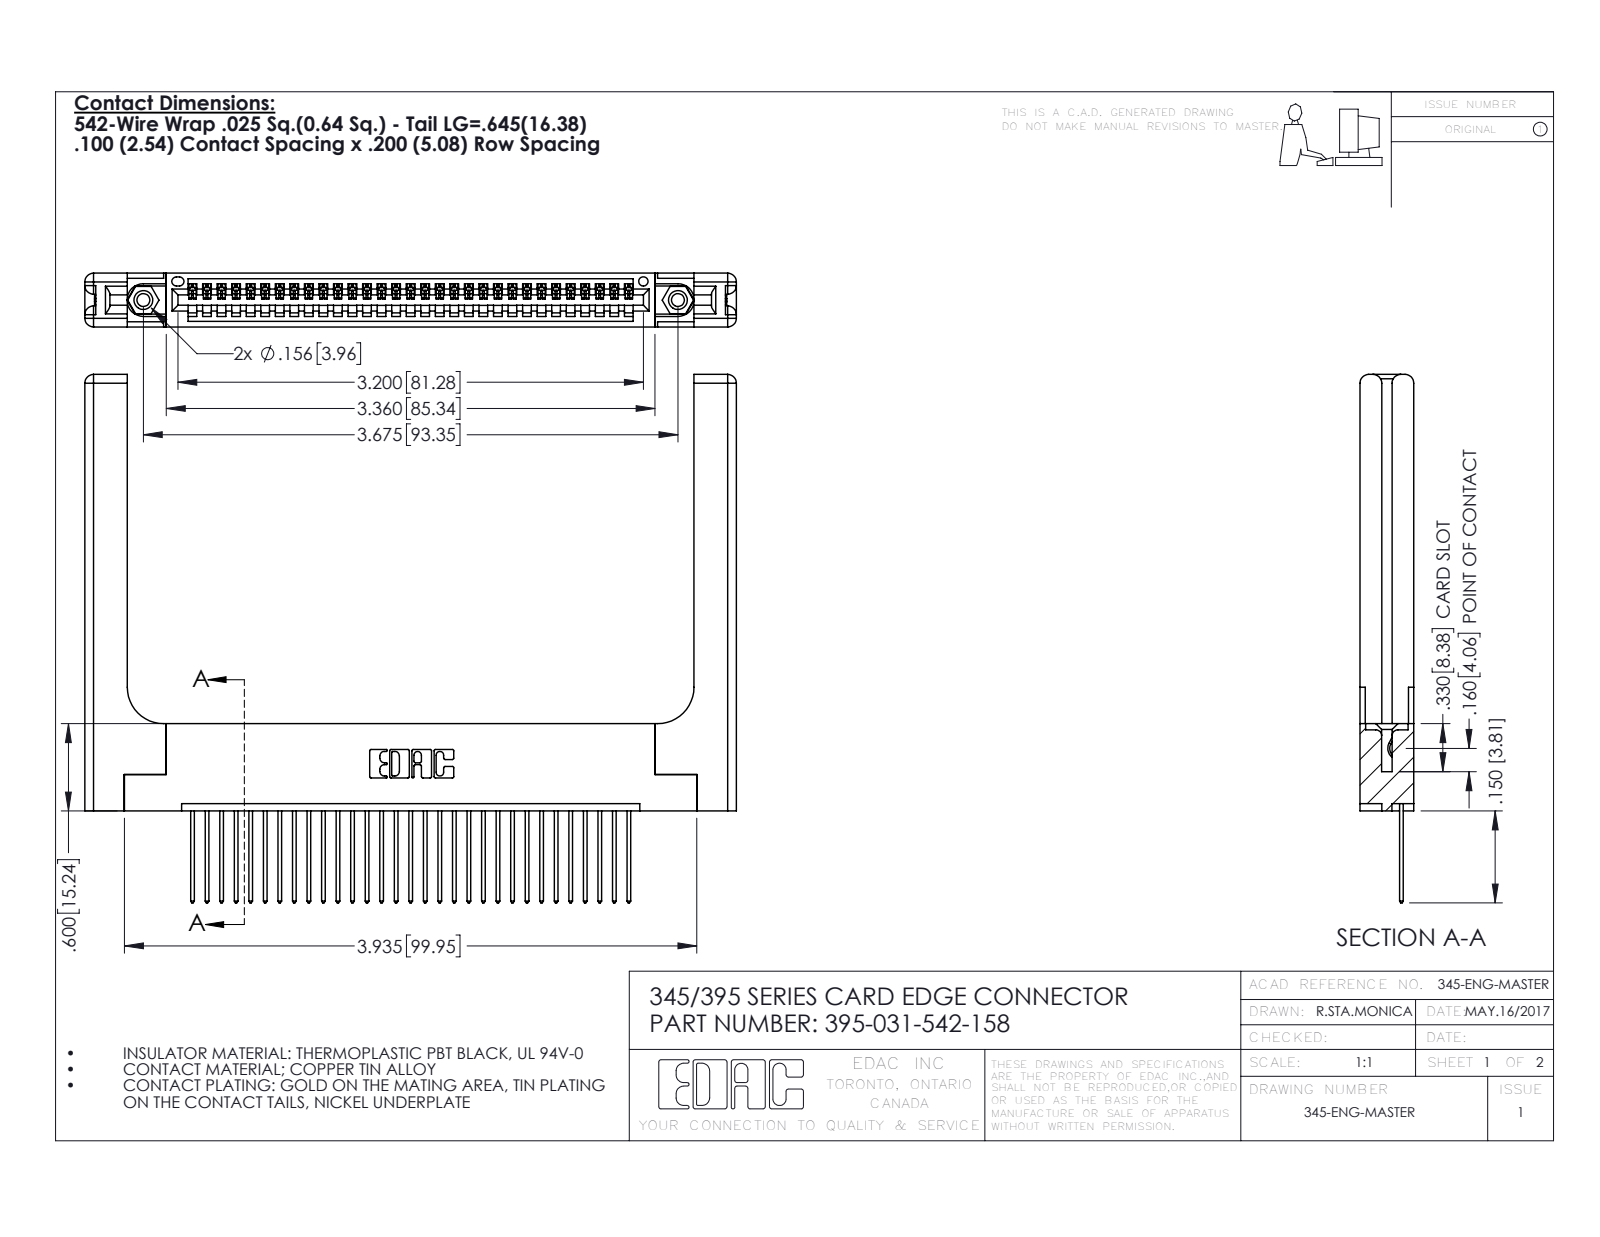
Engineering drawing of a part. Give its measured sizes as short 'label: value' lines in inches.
name: 345-220-058_345-220-058; 345-250-001_345-250-001-102; 345-292-001_345-293-142; 395-031-542-158 (+1 more)
written by: SolidWorks 2016 (CONFIG_CONTROL_DESIGN)
unit: in
bodies: 36 solids, 2180 faces (1468 planar, 652 cylindrical, 60 other)
size: 4.479 × 3.632 × 0.37
volume: 1.177 in³; area: 30.88 in²
holes: 2× ⌀0.089, 2× ⌀0.125, 2× ⌀0.156, 1× ⌀0.064
bosses: 2× ⌀0.155
rounds: 62× R0.006, 62× R0.01, 22× R0.01, 16× R0.06, 6× R0.007, 6× R0.031, 3× R0.026, 2× R0.03
face distances: 0.37, 0.072, 0.298, 0.2, 0.098, 0.272, 0.025, 0.148, 0.15, 0.077
hole spacings: 0.27, 3.44, 3.675
